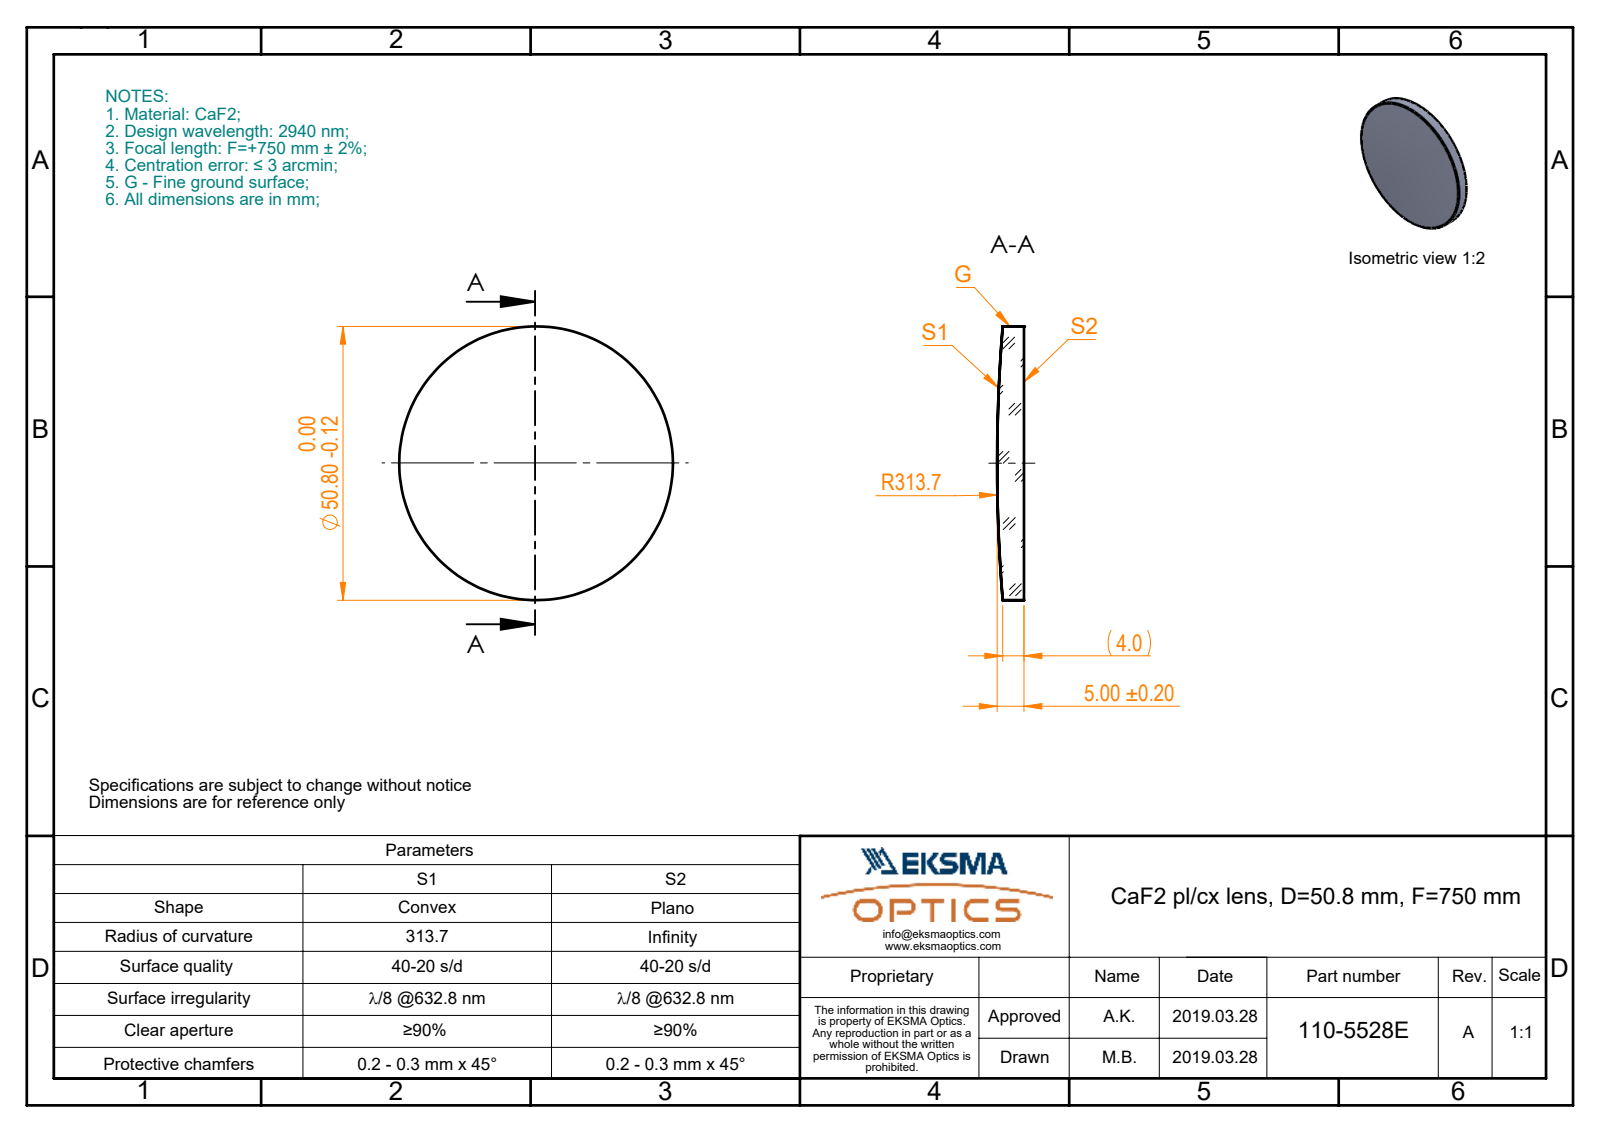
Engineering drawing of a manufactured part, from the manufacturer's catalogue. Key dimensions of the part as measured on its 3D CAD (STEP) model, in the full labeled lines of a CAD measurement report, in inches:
Part name (STEP PRODUCT): 110-5528E CaF2 pl-cx 50.8 F750
STEP written by: SolidWorks 2017 (CONFIG_CONTROL_DESIGN)
Units: inches
Bodies: 1 solid, 5 faces (1 planar, 2 cylindrical, 2 other)
Overall size (bounding box): 2 × 2 × 0.197
Volume: 0.555 in³ · Surface area: 7.271 in²
Round bosses / shafts (diameter × count): ⌀2 ×1
